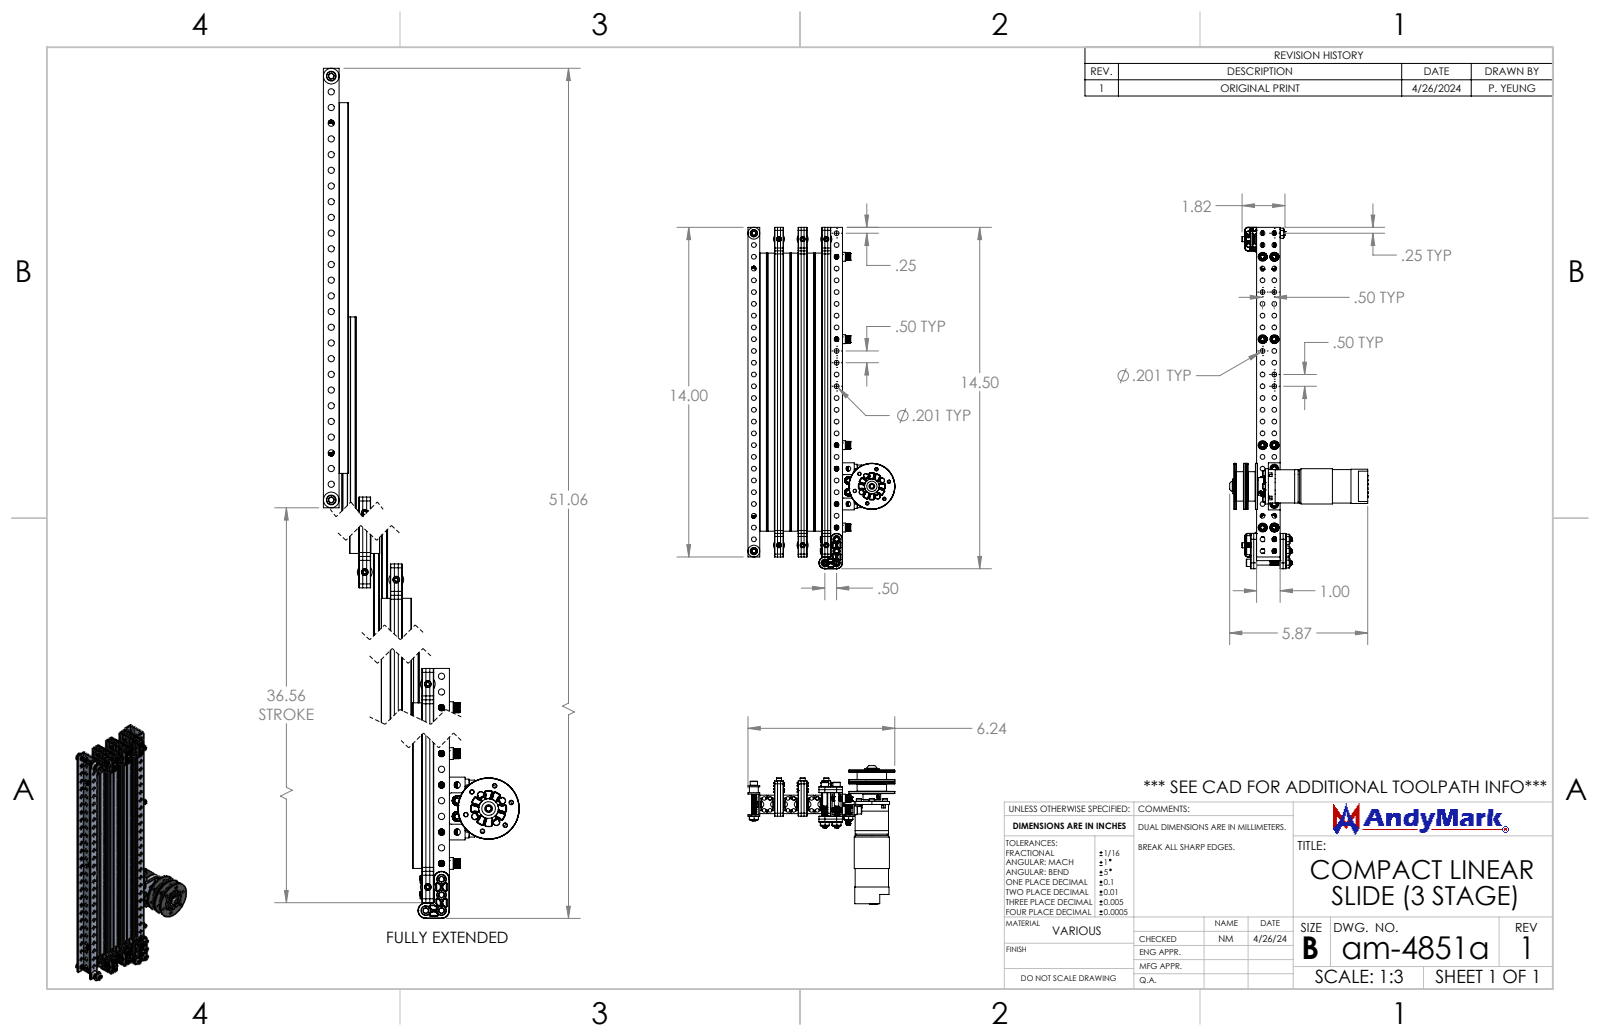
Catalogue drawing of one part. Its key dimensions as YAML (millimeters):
part_name: "NeveRest Orbital 2 Stage Gearbox 6mm D; SHCS M3 x 8mm with patch am-1500_am-1500 M3x8mm SHCS (Patched); SAR330_3; am-1026 #10 Flat Washer_am-1026 #10 Flat Washer (+8 more)"
step_written_by: "SolidWorks 2024 (AUTOMOTIVE_DESIGN)"
units: millimeters
bodies: {solids: 318, faces: 38887, planar: 6948, cylindrical: 13552, other: 18387}
overall_size: [368.3, 158.5, 149.2]
volume: 564000
surface_area: 521400
round_holes:
  - {diameter: 5.1, count: 122}
  - {diameter: 4.2, count: 80}
  - {diameter: 3.2, count: 20}
  - {diameter: 4.1, count: 20}
  - {diameter: 6.1, count: 20}
  - {diameter: 3.2, count: 13}
  - {diameter: 2.5, count: 10}
  - {diameter: 4.9, count: 10}
  - {diameter: 8, count: 7}
  - {diameter: 4.3, count: 6}
  - {diameter: 6.7, count: 6}
  - {diameter: 7.2, count: 6}
round_bosses_or_shafts:
  - {diameter: 4.8, count: 21}
  - {diameter: 3, count: 15}
  - {diameter: 5.5, count: 14}
  - {diameter: 9.5, count: 12}
  - {diameter: 2.4, count: 12}
  - {diameter: 8, count: 10}
  - {diameter: 7.9, count: 10}
  - {diameter: 12, count: 7}
partial_cylinders:
  - {radius: 0.3, count: 4052}
  - {radius: 0.2, count: 120}
  - {radius: 1.6, count: 34}
  - {radius: 0.8, count: 32}
  - {radius: 1.9, count: 24}
  - {radius: 2.1, count: 20}
  - {radius: 3.2, count: 14}
  - {radius: 2.3, count: 8}
face_to_face_distances: [25.5, 51.1, 25.5, 16, 2.7, 22.7, 1.4, 14.6, 12.7, 1.6]
hole_center_spacings: [12.7, 25.4, 38.1, 50.8, 63.5, 76.2, 88.9, 101.6]
